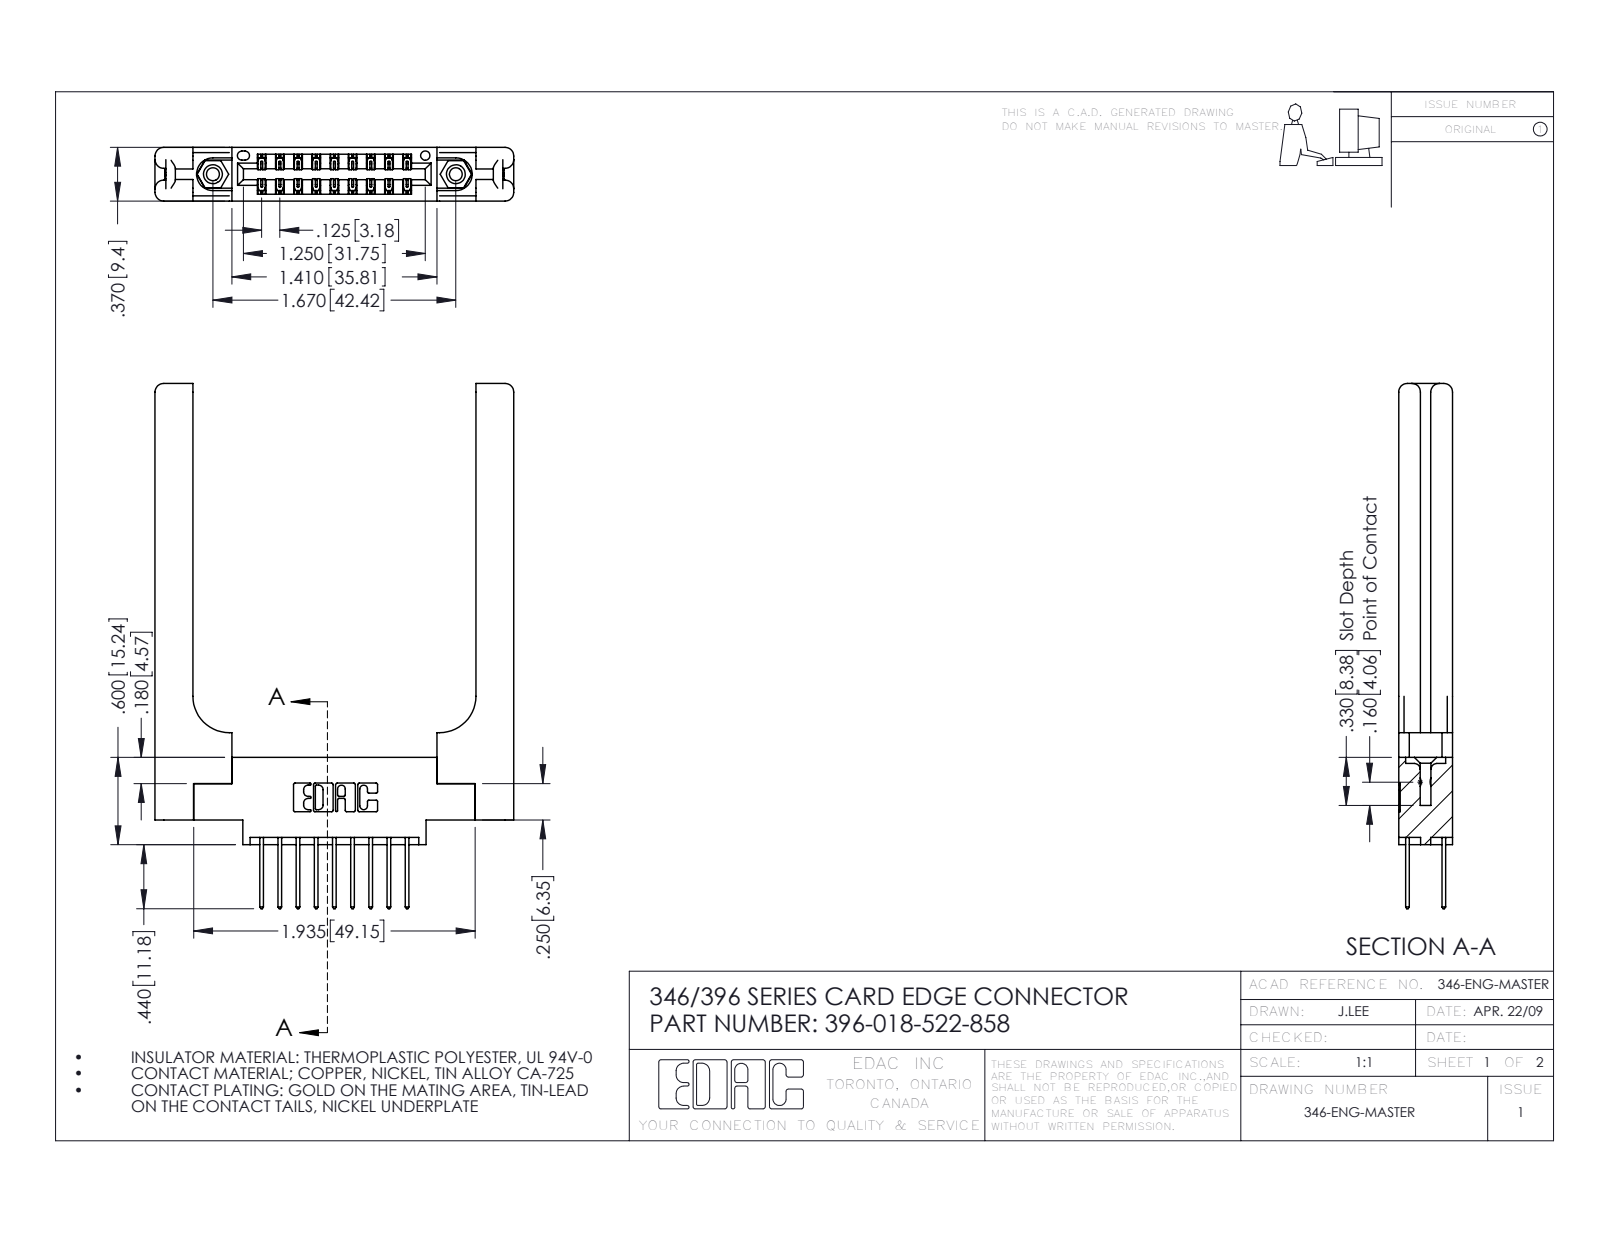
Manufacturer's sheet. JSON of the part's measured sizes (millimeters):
{"part_name": "346-220-058_345-220-058; 345-292-001_345-293-122; 345-250-001_345-250-001-102; 396-018-522-858 (+1 more)", "step_written_by": "SolidWorks 2016 (CONFIG_CONTROL_DESIGN)", "units": "millimeters", "bodies": {"solids": 23, "faces": 1318, "planar": 858, "cylindrical": 400, "other": 60}, "overall_size": [91.7, 62.6, 9.4], "volume_mm3": 13200, "surface_area_mm2": 12740, "round_holes": [[2.3, 2], [3.2, 2], [4, 2], [1.6, 1]], "round_bosses_or_shafts": [[3.9, 2]], "partial_cylinders_radius": [[0.2, 27], [0.3, 22], [0.3, 18], [1.5, 16], [0.2, 6], [0.8, 6], [0.7, 3], [0.4, 2]], "face_to_face_distances": [9.4, 3.8, 1.8, 3.8, 5.6, 2.6, 1.2, 8.2, 4.4, 6.4], "hole_center_spacings": [6.2, 37.2, 42.4]}
